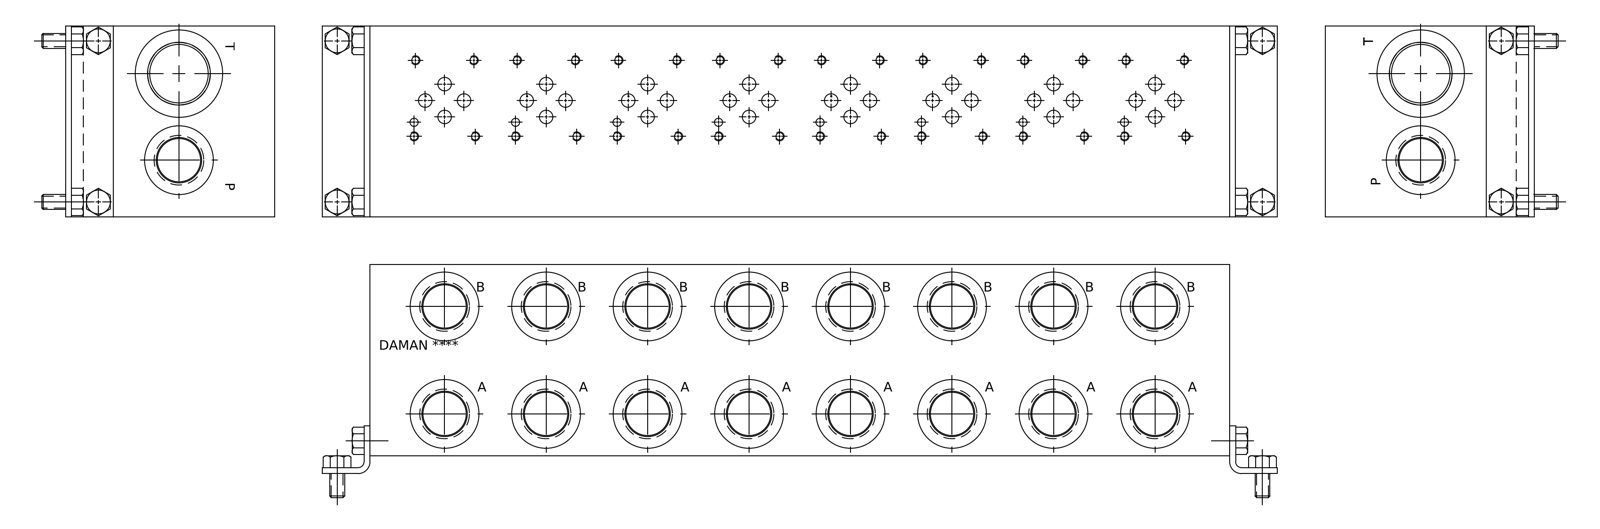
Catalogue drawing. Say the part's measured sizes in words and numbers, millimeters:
The part is named "D03HP082B". Its 3-D file was written by "Autodesk Inventor 2021 (AUTOMOTIVE_DESIGN)". It is 1 solid with 1098 faces: 551 planar, 192 cylindrical and 355 other. Overall it measures 457.2 by 101.6 by 101.6 millimeters. Its volume is 4 354 000 cubic millimeters and its surface area 270 254 square millimeters. Round holes: 32 of diameter 4.22, 32 of diameter 5, 24 of diameter 6.35, 17 of diameter 24.41, 17 of diameter 26.54, 17 of diameter 37.11, 9 of diameter 23.01, 8 of diameter 3.96, 8 of diameter 7.14, 8 of diameter 10.72, 2 of diameter 6.76, 2 of diameter 8. The main face-to-face distances are 101.6, 0.79, 100.81, 457.2, 456.41, 17.88, 17.09, 455.62, 83.72, 0.75. The hole center spacings are 107.95, 215.9, 53.97, 53.98, 78.61, 161.93, 122.14, 161.92.
